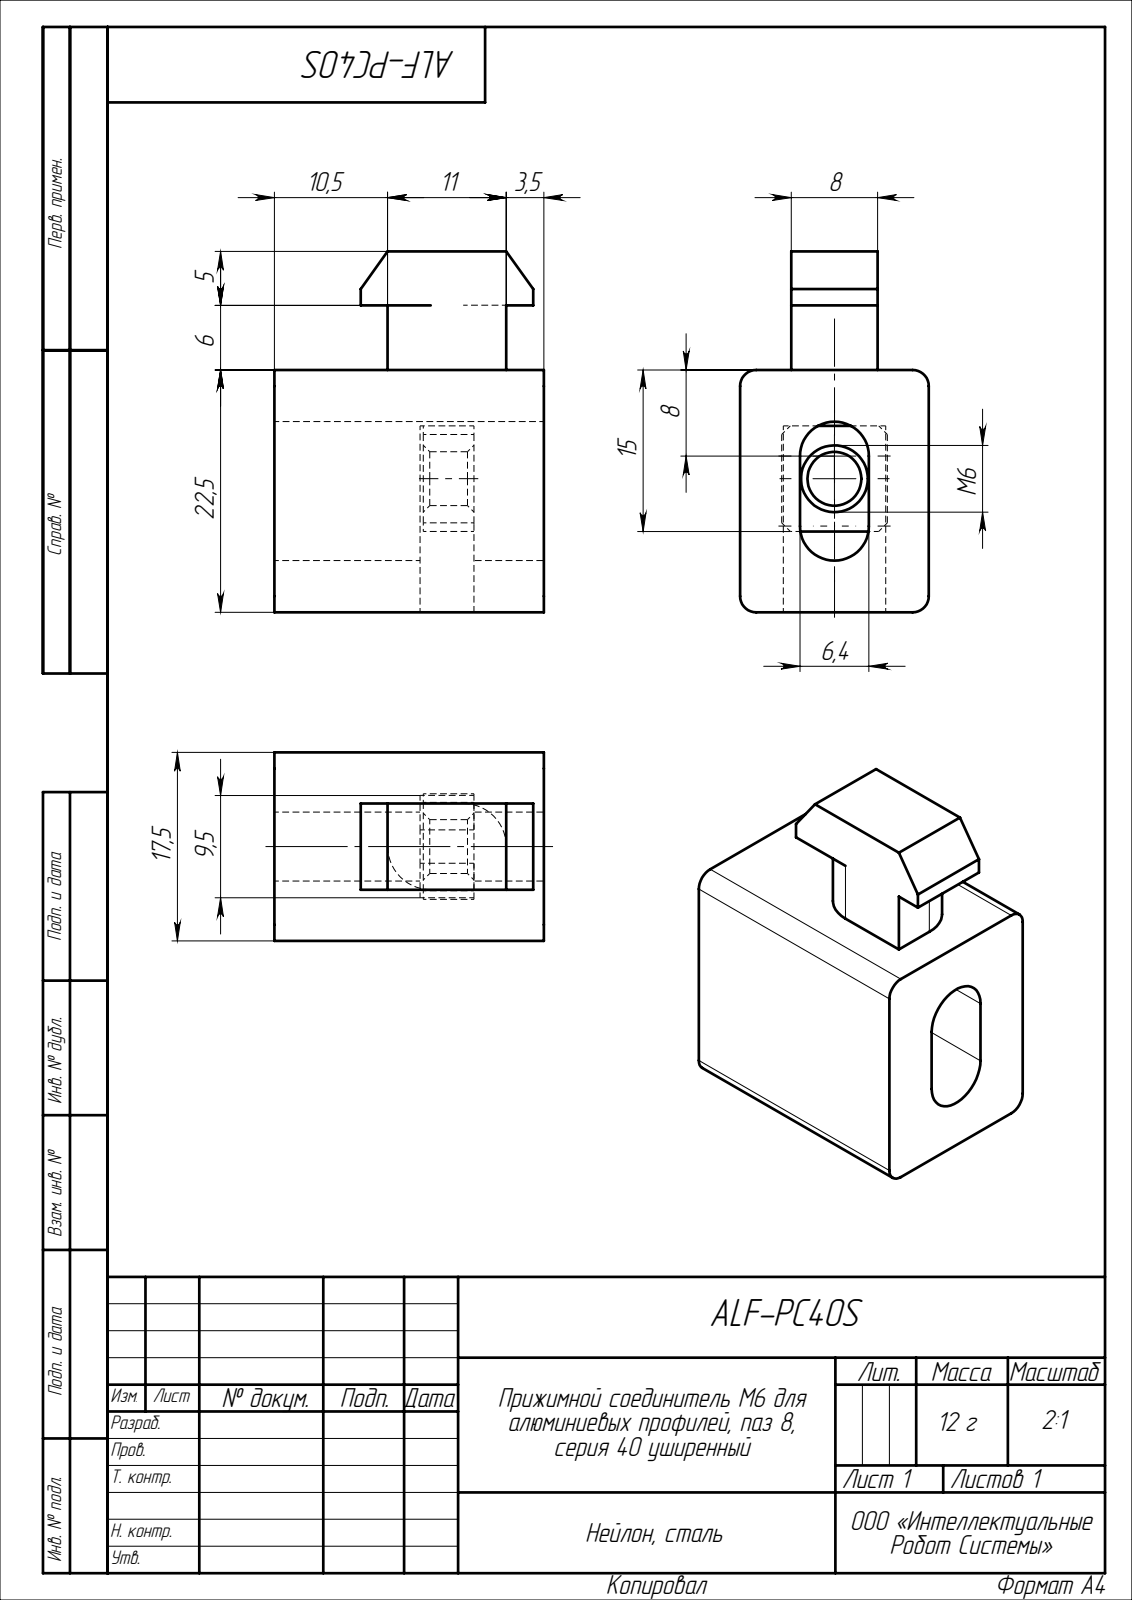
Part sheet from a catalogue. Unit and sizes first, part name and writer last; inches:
Units: inches
Overall size (bounding box): 1.319 × 0.984 × 0.689
Round holes (diameter × count): ⌀0.197 ×1
Partial cylindrical surfaces — rounded edges, fillets, slot ends (radius × count): R0.059 ×4, R0.126 ×2, R0.157 ×2
Main face-to-face distances: 0.689, 0.984, 0.531, 0.886, 0.219, 0.47, 0.187, 0.502, 0.031, 0.283
Volume: 0.543 in³ · Surface area: 6.938 in²
Bodies: 2 solids, 52 faces (37 planar, 11 cylindrical, 4 other)
Part name (STEP PRODUCT): ALF-PC40S; Соединитель^ALF-PC40S; Копия Гайка^ALF-PC40S
STEP written by: SolidWorks 2022 (CONFIG_CONTROL_DESIGN)
